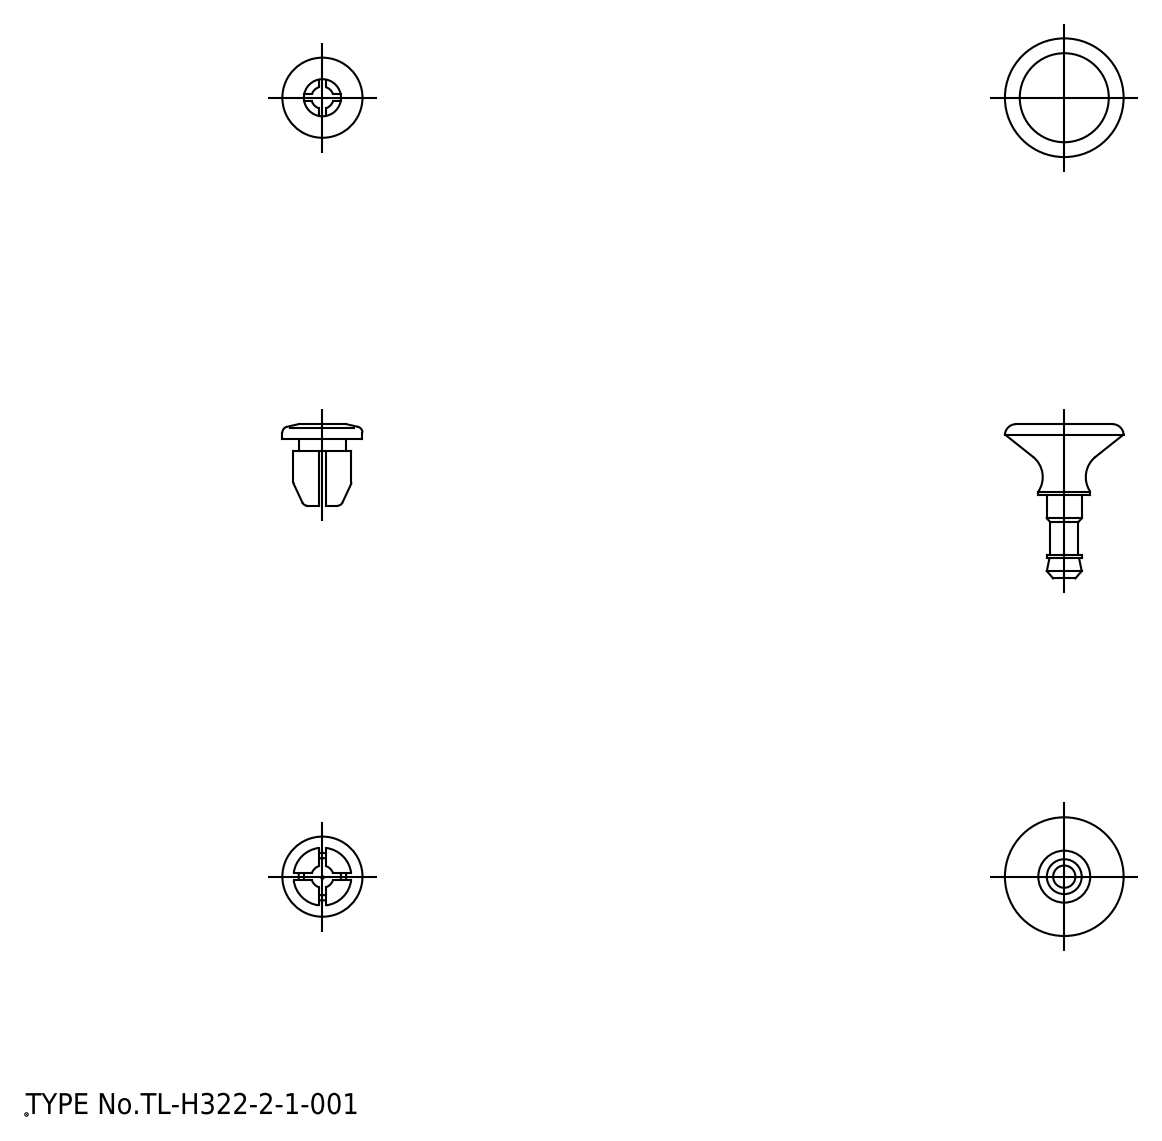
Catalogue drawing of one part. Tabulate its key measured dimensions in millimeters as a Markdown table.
| quantity | value |
| --- | --- |
| part name | grommet; plunger |
| STEP written by | spGate 18.9.1 (****-****-****-****) (AUTOMOTIVE_DESIGN) |
| units | millimeters |
| bodies | 2 solids, 81 faces (31 planar, 22 cylindrical, 28 other) |
| overall size | 22.3 × 16 × 16 |
| volume | 1 241 mm³ |
| surface area | 1 336 mm² |
| round holes (diameter × count) | 5 × 1 |
| round bosses / shafts (diameter × count) | 10.9 × 1, 7.8 × 1, 7 × 1, 6.4 × 1, 4.7 × 1, 3.8 × 1 |
| partial cylindrical surfaces (radius × count) | 1.5 × 1 |
| main face-to-face distances | 13.3, 1, 3.8, 9.5, 1.6, 5.4, 14.9, 6, 7.6, 11.4 |
